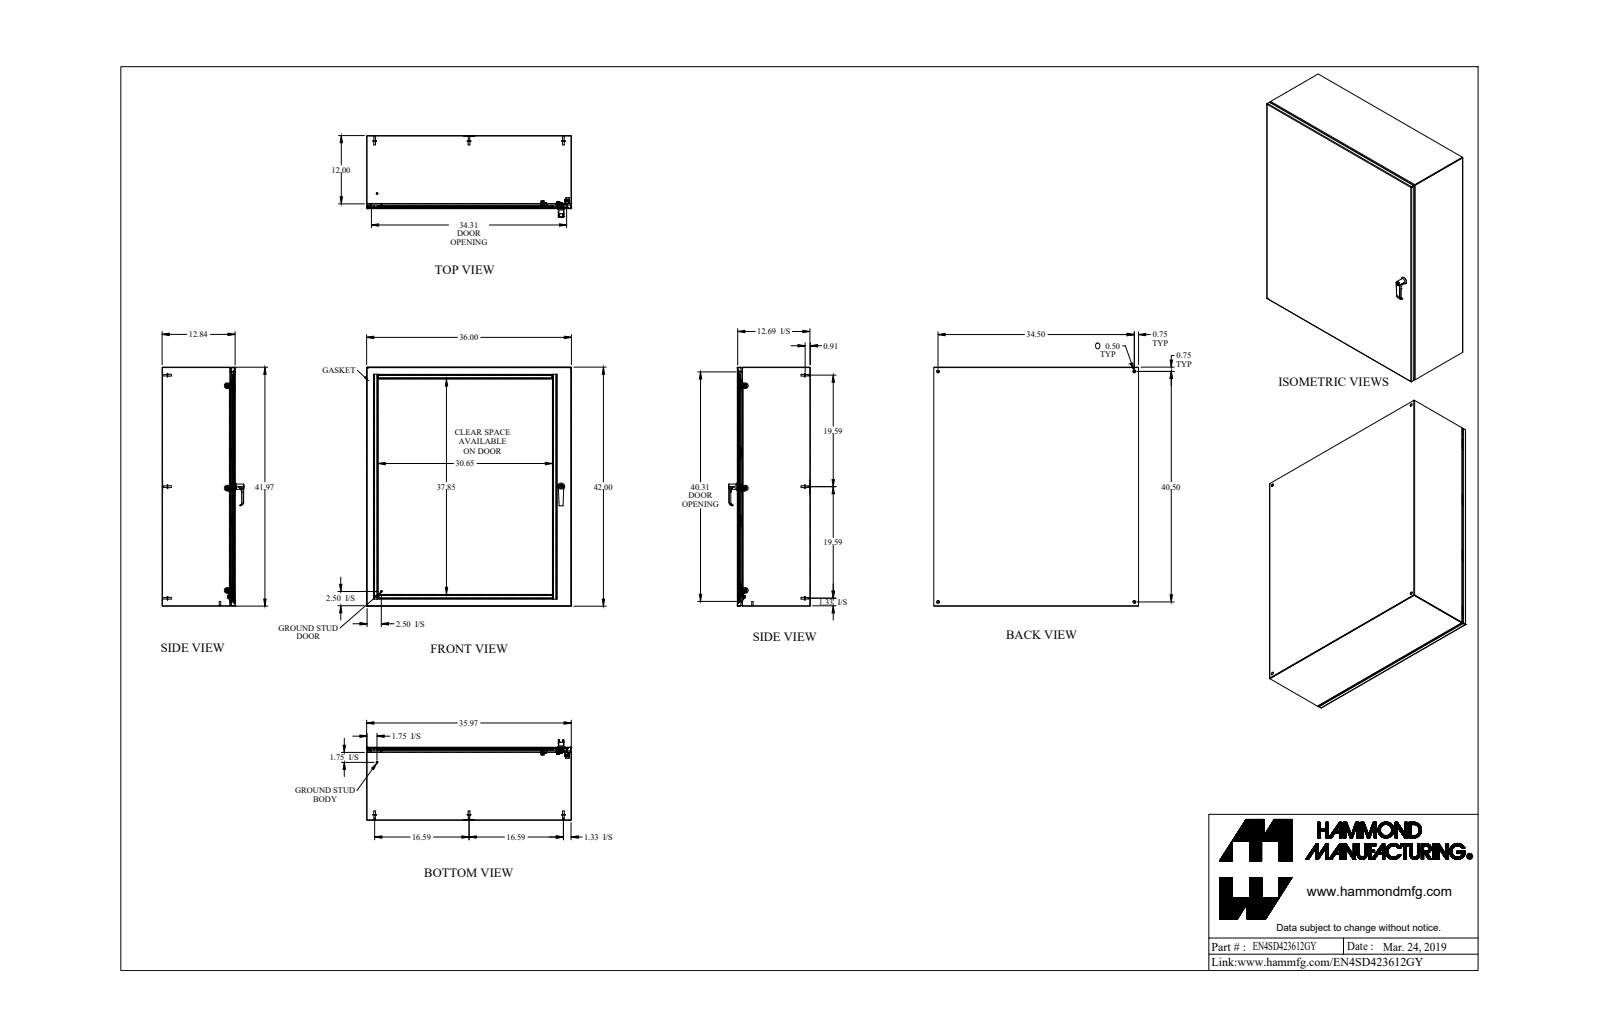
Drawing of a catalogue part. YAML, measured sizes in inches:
part_name: "EN4SD423612GY"
step_written_by: "SolidWorks 2018 (AUTOMOTIVE_DESIGN)"
units: inches
bodies: {solids: 63, faces: 1719, planar: 757, cylindrical: 632, other: 330}
overall_size: [42, 36, 14.367]
volume: 408.9
surface_area: 11443
round_holes:
  - {diameter: 0.176, count: 6}
  - {diameter: 0.196, count: 4}
  - {diameter: 0.5, count: 4}
  - {diameter: 0.25, count: 3}
  - {diameter: 0.265, count: 3}
  - {diameter: 0.413, count: 3}
  - {diameter: 0.256, count: 2}
  - {diameter: 0.313, count: 2}
  - {diameter: 0.394, count: 2}
  - {diameter: 0.172, count: 1}
  - {diameter: 0.24, count: 1}
  - {diameter: 0.242, count: 1}
round_bosses_or_shafts:
  - {diameter: 0.313, count: 8}
  - {diameter: 0.27, count: 8}
  - {diameter: 0.625, count: 7}
  - {diameter: 0.25, count: 7}
  - {diameter: 0.375, count: 6}
  - {diameter: 0.156, count: 6}
  - {diameter: 1, count: 3}
  - {diameter: 0.63, count: 2}
partial_cylinders:
  - {radius: 0.043, count: 24}
  - {radius: 0.081, count: 24}
  - {radius: 0.036, count: 18}
  - {radius: 0.108, count: 18}
  - {radius: 0.03, count: 15}
  - {radius: 0.062, count: 13}
  - {radius: 0.094, count: 10}
  - {radius: 0.016, count: 9}
face_to_face_distances: [0.072, 12.765, 12.693, 12.837, 35.928, 41.928, 35.856, 36, 41.856, 42]
hole_center_spacings: [0.787, 35.969, 17.981, 17.988, 18, 33.504, 34.5, 40.5]
